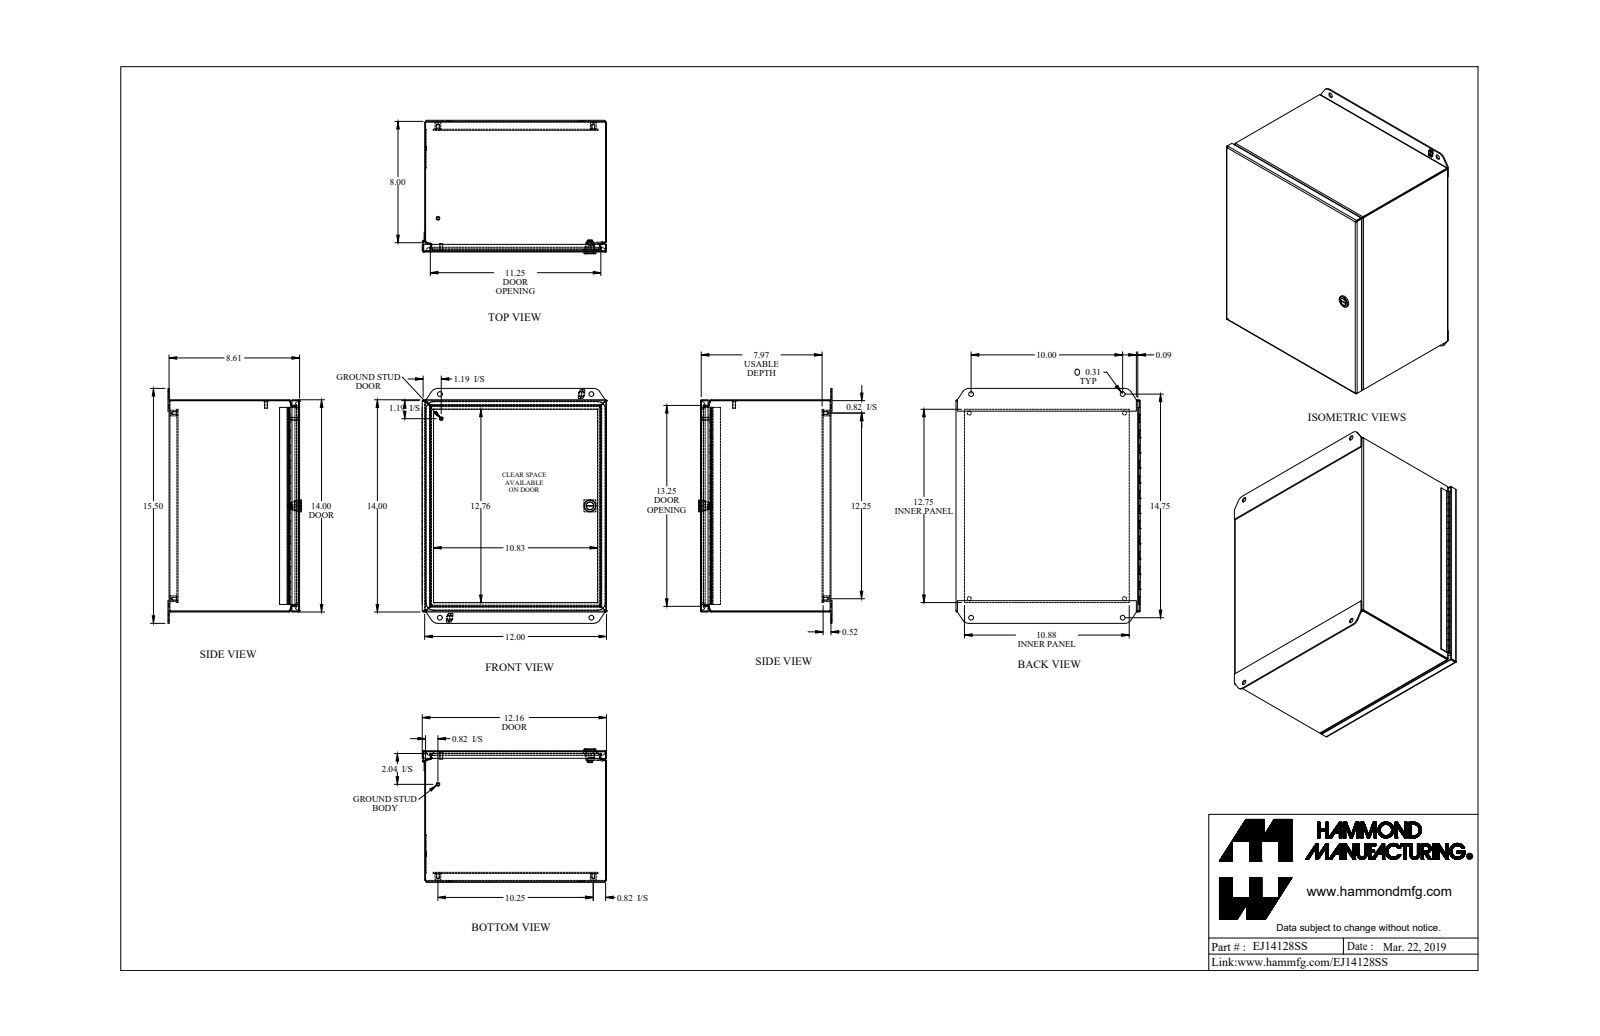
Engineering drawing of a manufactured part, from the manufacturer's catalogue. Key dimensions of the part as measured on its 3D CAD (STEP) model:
Part name (STEP PRODUCT): EJ14128SS_Default
STEP written by: SolidWorks 2019 (CONFIG_CONTROL_DESIGN)
Units: inches
Bodies: 16 solids, 752 faces (418 planar, 238 cylindrical, 96 other)
Overall size (bounding box): 15.5 × 12.165 × 8.805
Volume: 64.07 in³ · Surface area: 2 130 in²
Round holes (diameter × count): ⌀0.156 ×4, ⌀0.265 ×4, ⌀0.313 ×4, ⌀0.05 ×1, ⌀0.516 ×1
Round bosses / shafts (diameter × count): ⌀0.375 ×4, ⌀0.25 ×2, ⌀0.19 ×2, ⌀0.788 ×1, ⌀0.535 ×1, ⌀0.496 ×1, ⌀0.435 ×1, ⌀0.1 ×1
Partial cylindrical surfaces — rounded edges, fillets, slot ends (radius × count): R0.029 ×16, R0.086 ×16, R0.281 ×12, R0.25 ×4, R0.499 ×4, R0.5 ×4, R0.06 ×2, R0.03 ×1
Main face-to-face distances: 0.057, 8.554, 11.943, 13.943, 0.072, 0.589, 8.611, 8.497, 8.094, 8.037
Hole centre spacings: 1.257, 10.202, 13.5, 16.875, 6.129, 7.376, 10, 10.25
